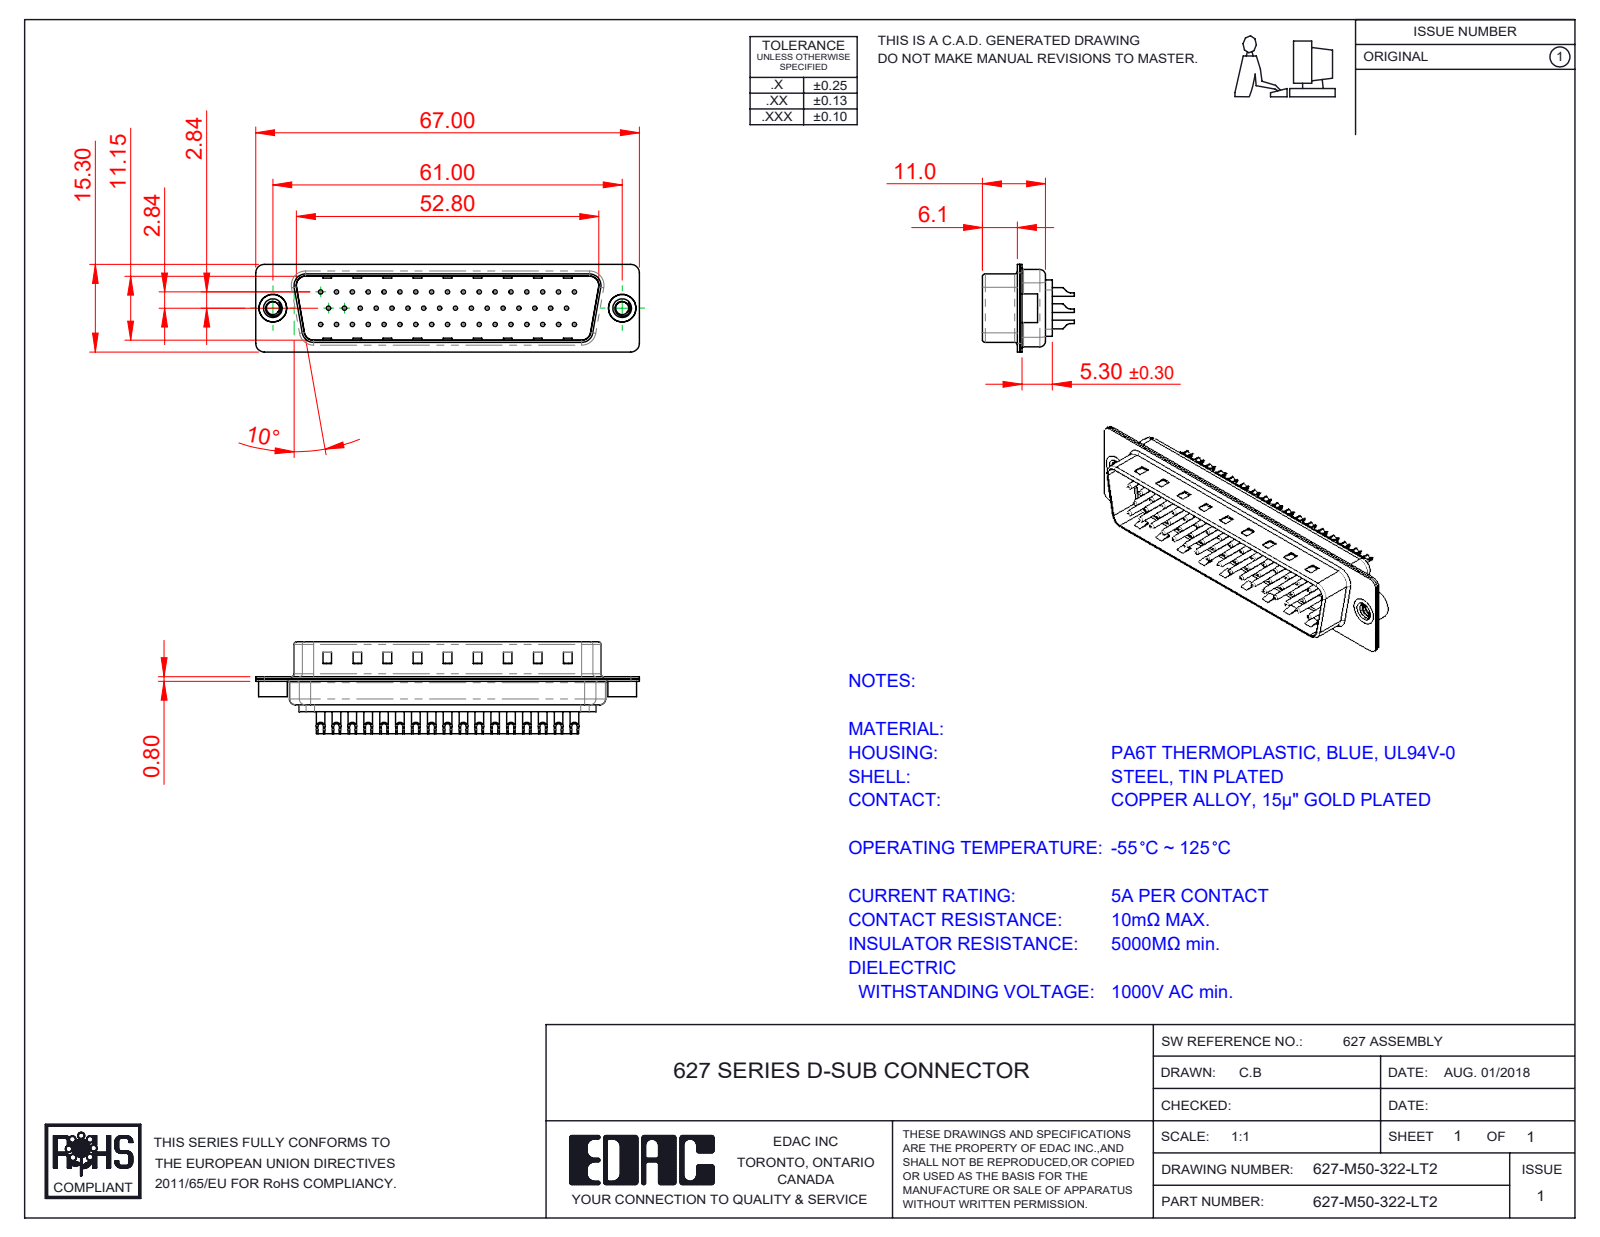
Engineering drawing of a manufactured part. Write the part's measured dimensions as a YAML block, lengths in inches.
part_name: "627M Housing_50 Contacts; 627M Contact Row 3_22; 627M Contact Row 1_22; 627M Contact Row 2_22L (+4 more)"
step_written_by: "SolidWorks 2020 (CONFIG_CONTROL_DESIGN)"
units: inches
bodies: {solids: 55, faces: 2262, planar: 653, cylindrical: 941, other: 668}
overall_size: [2.638, 0.632, 0.602]
volume: 0.283
surface_area: 17.31
round_holes:
  - {diameter: 0.03, count: 50}
  - {diameter: 0.039, count: 50}
  - {diameter: 0.063, count: 50}
  - {diameter: 0.079, count: 50}
  - {diameter: 0.089, count: 2}
  - {diameter: 0.157, count: 2}
  - {diameter: 0.189, count: 2}
round_bosses_or_shafts:
  - {diameter: 0.059, count: 50}
  - {diameter: 0.197, count: 2}
  - {diameter: 0.193, count: 2}
partial_cylinders:
  - {radius: 0.059, count: 16}
  - {radius: 0.079, count: 12}
  - {radius: 0.02, count: 8}
  - {radius: 0.063, count: 8}
  - {radius: 0.039, count: 7}
  - {radius: 0.01, count: 4}
  - {radius: 0.024, count: 4}
  - {radius: 0.026, count: 4}
face_to_face_distances: [0.016, 0.455, 0.224, 0.24, 0.031, 0.03, 0.485, 0.485, 0.516, 0.209]
hole_center_spacings: [0.124, 0.109, 0.218, 0.327, 0.436, 0.545, 0.654, 0.198]
